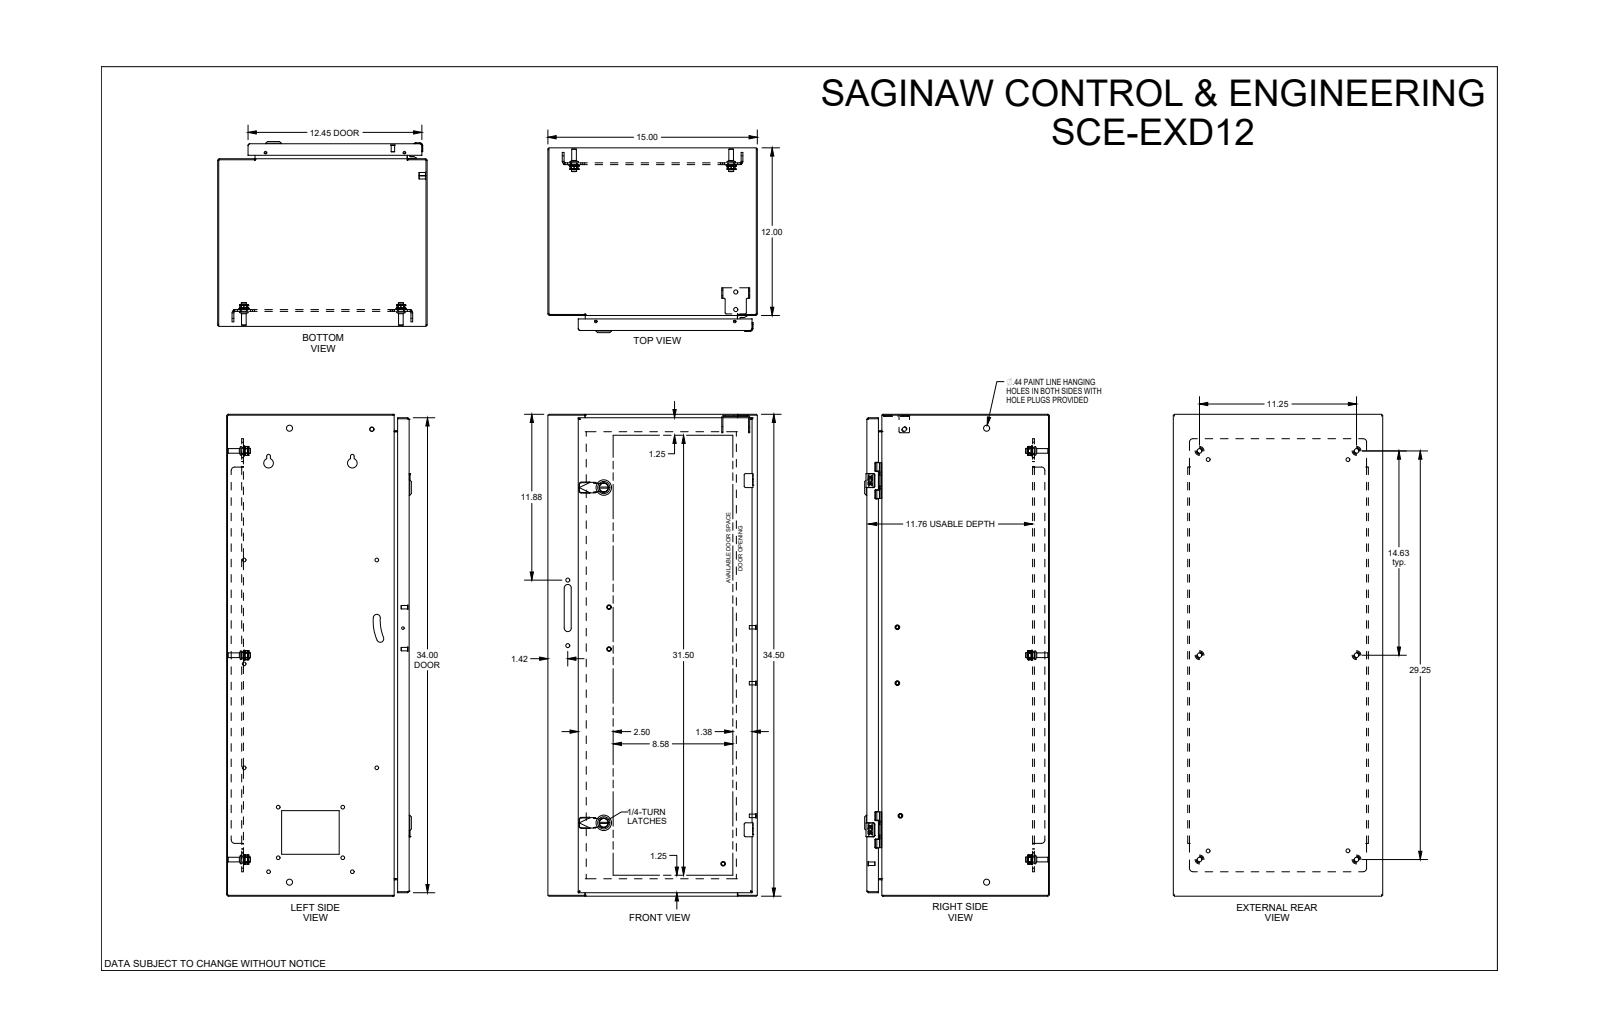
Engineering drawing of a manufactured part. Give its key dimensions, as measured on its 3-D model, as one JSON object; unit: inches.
{"part_name": "SCE-EXD12", "step_written_by": "SolidWorks 2019 (CONFIG_CONTROL_DESIGN)", "units": "inches", "bodies": {"solids": 0, "faces": 2431, "planar": 1174, "cylindrical": 757, "other": 500}, "overall_size": [34.5, 15, 13.23], "round_holes": [[0.266, 15], [0.367, 6], [0.5, 6], [0.375, 5], [0.172, 4], [0.205, 4], [0.244, 4], [0.28, 4], [0.296, 3], [0.04, 2], [0.156, 2], [0.197, 2]], "round_bosses_or_shafts": [[0.366, 6], [0.332, 6], [0.248, 6], [0.17, 6], [0.25, 4], [0.24, 4], [0.196, 3], [1.102, 2]], "partial_cylinders_radius": [[0.012, 56], [0.015, 40], [0.01, 36], [0.02, 20], [0.117, 14], [0.025, 12], [0.042, 12], [0.1, 12]], "face_to_face_distances": [0.075, 12.998, 14.925, 0.075, 12.923, 13.073, 1.125, 14.85, 1, 11.923], "hole_center_spacings": [25, 14.625, 18.452, 29.25, 3.377, 11.25, 11.25, 12.187]}
